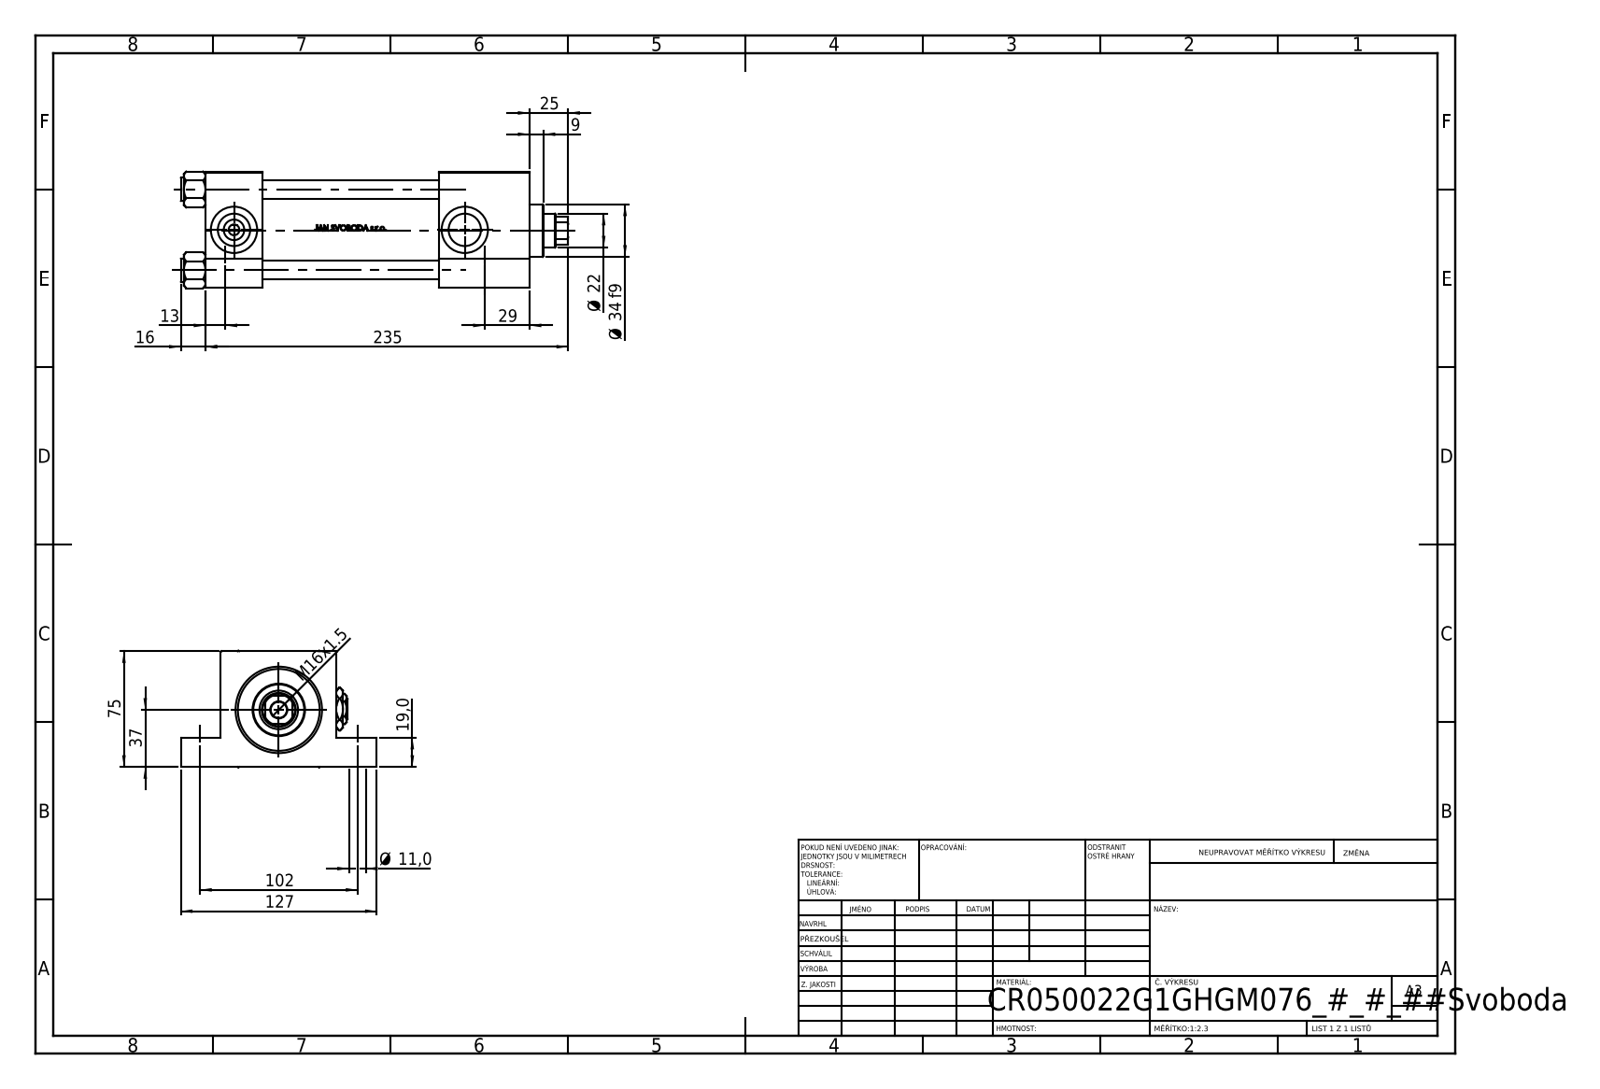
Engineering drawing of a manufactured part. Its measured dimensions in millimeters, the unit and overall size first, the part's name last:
Units: millimetres
Overall size (bounding box): 251 × 127 × 75.54
Round holes (diameter × count): ⌀11 ×4, ⌀12 ×4, ⌀7 ×2, ⌀20.96 ×2, ⌀30 ×2, ⌀10.5 ×1, ⌀22 ×1, ⌀25 ×1, ⌀41 ×1, ⌀50 ×1, ⌀53 ×1
Round bosses / shafts (diameter × count): ⌀15 ×4, ⌀56 ×1, ⌀34 ×1
Partial cylindrical surfaces — rounded edges, fillets, slot ends (radius × count): R10.5 ×1
Main face-to-face distances: 75, 37, 210, 173, 19, 56, 151, 114, 59, 26
Hole centre spacings: 52.3, 36.63, 37.34, 73.96, 102, 168, 196.54, 149.5
Volume: 826 997 mm³ · Surface area: 192 267 mm²
Bodies: 12 solids, 1134 faces (454 planar, 128 cylindrical, 552 other)
Part name (STEP PRODUCT): V215CR_VCP_G; NUT_M5_G; Zatka_pro_OIL_PORT; V215CR_G_Body (+2 more)
STEP written by: SolidWorks 2019 (CONFIG_CONTROL_DESIGN)
